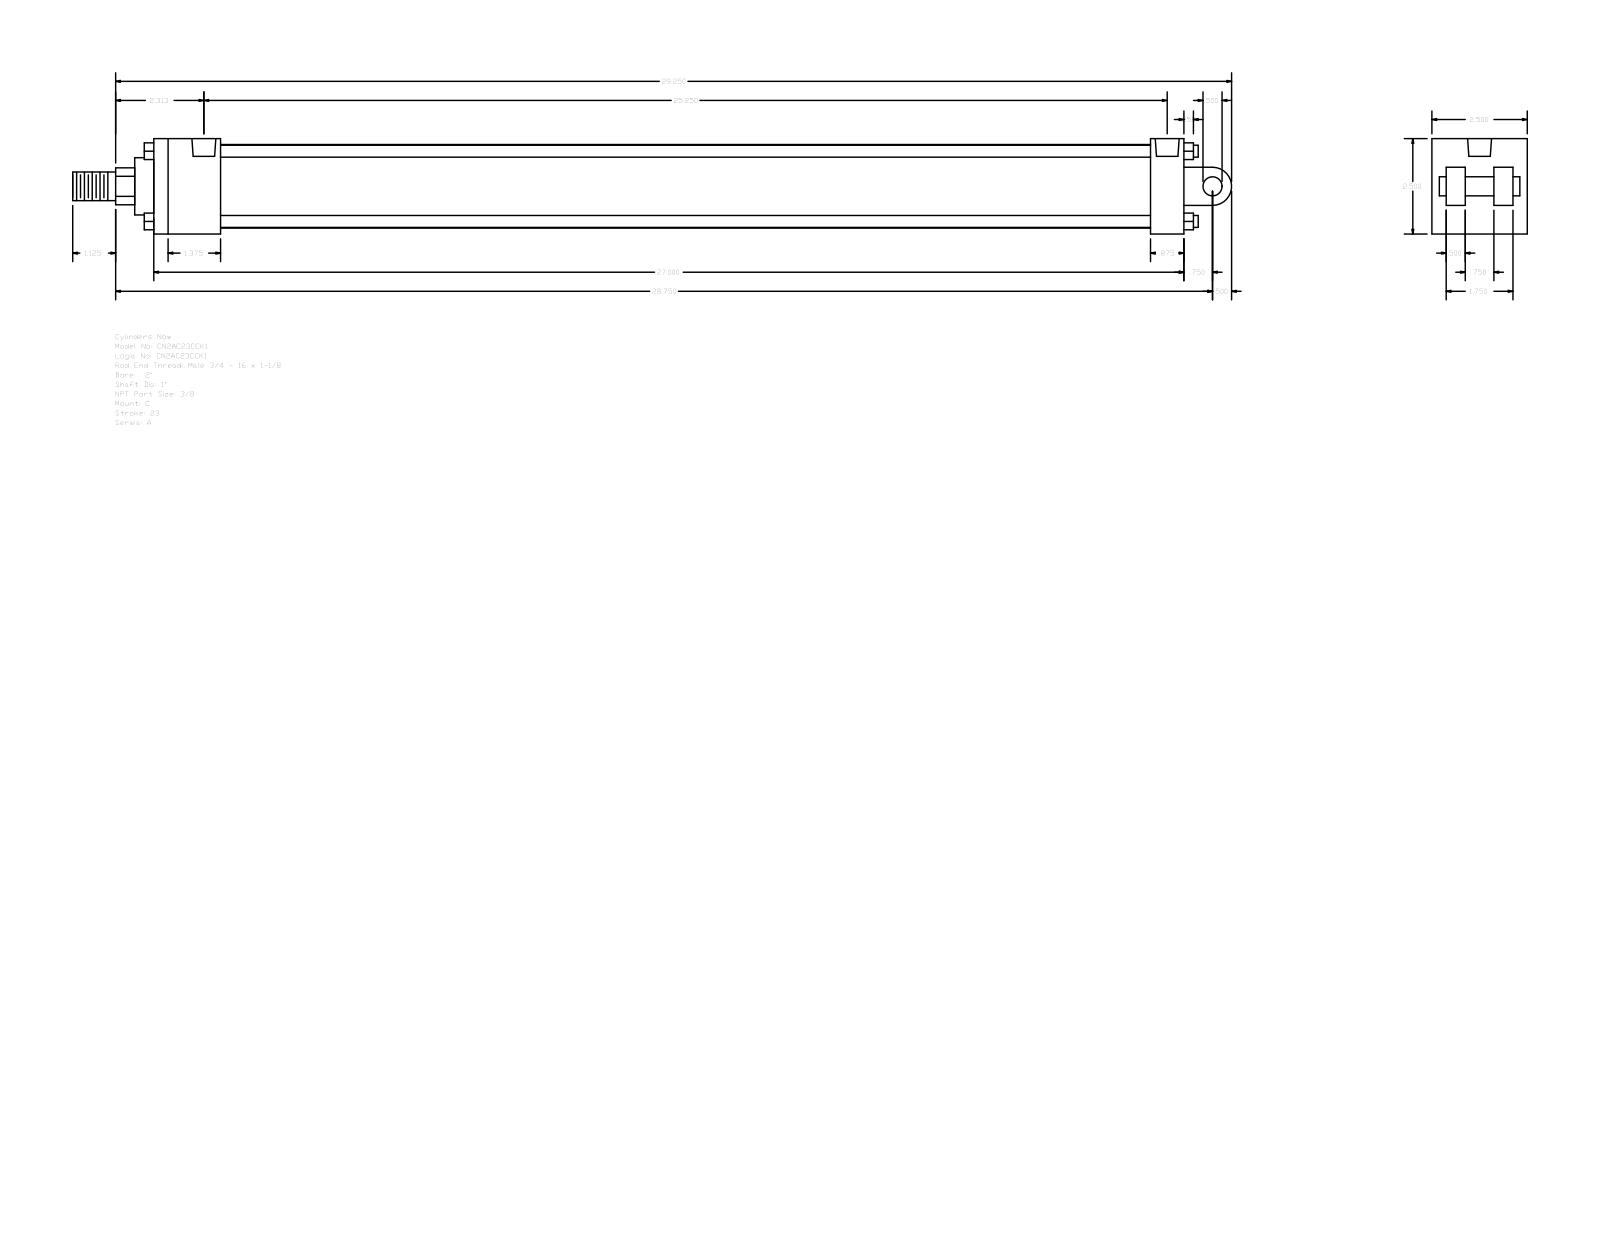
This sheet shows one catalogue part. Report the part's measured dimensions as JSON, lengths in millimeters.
{"part_name": "A_C__0200_1", "step_written_by": "GSSL Pune (CONFIG_CONTROL_DESIGN)", "units": "millimeters", "bodies": {"solids": 0, "faces": 135, "planar": 102, "cylindrical": 33, "other": 0}, "overall_size": [771.52, 63.5, 63.5], "round_holes": [[5.56, 4], [15.93, 2]], "round_bosses_or_shafts": [[7.94, 4], [55.63, 1], [38.1, 1], [25.4, 1], [19.05, 1], [12.7, 1]], "partial_cylinders_radius": [[12.29, 1], [12.7, 1]], "face_to_face_distances": [63.5, 22.22, 685.8, 44.45, 12.7, 641.35, 663.58, 619.13, 9.52, 53.98], "hole_center_spacings": [635.78, 1.59, 3.98, 637.37, 639.76, 641.35]}
